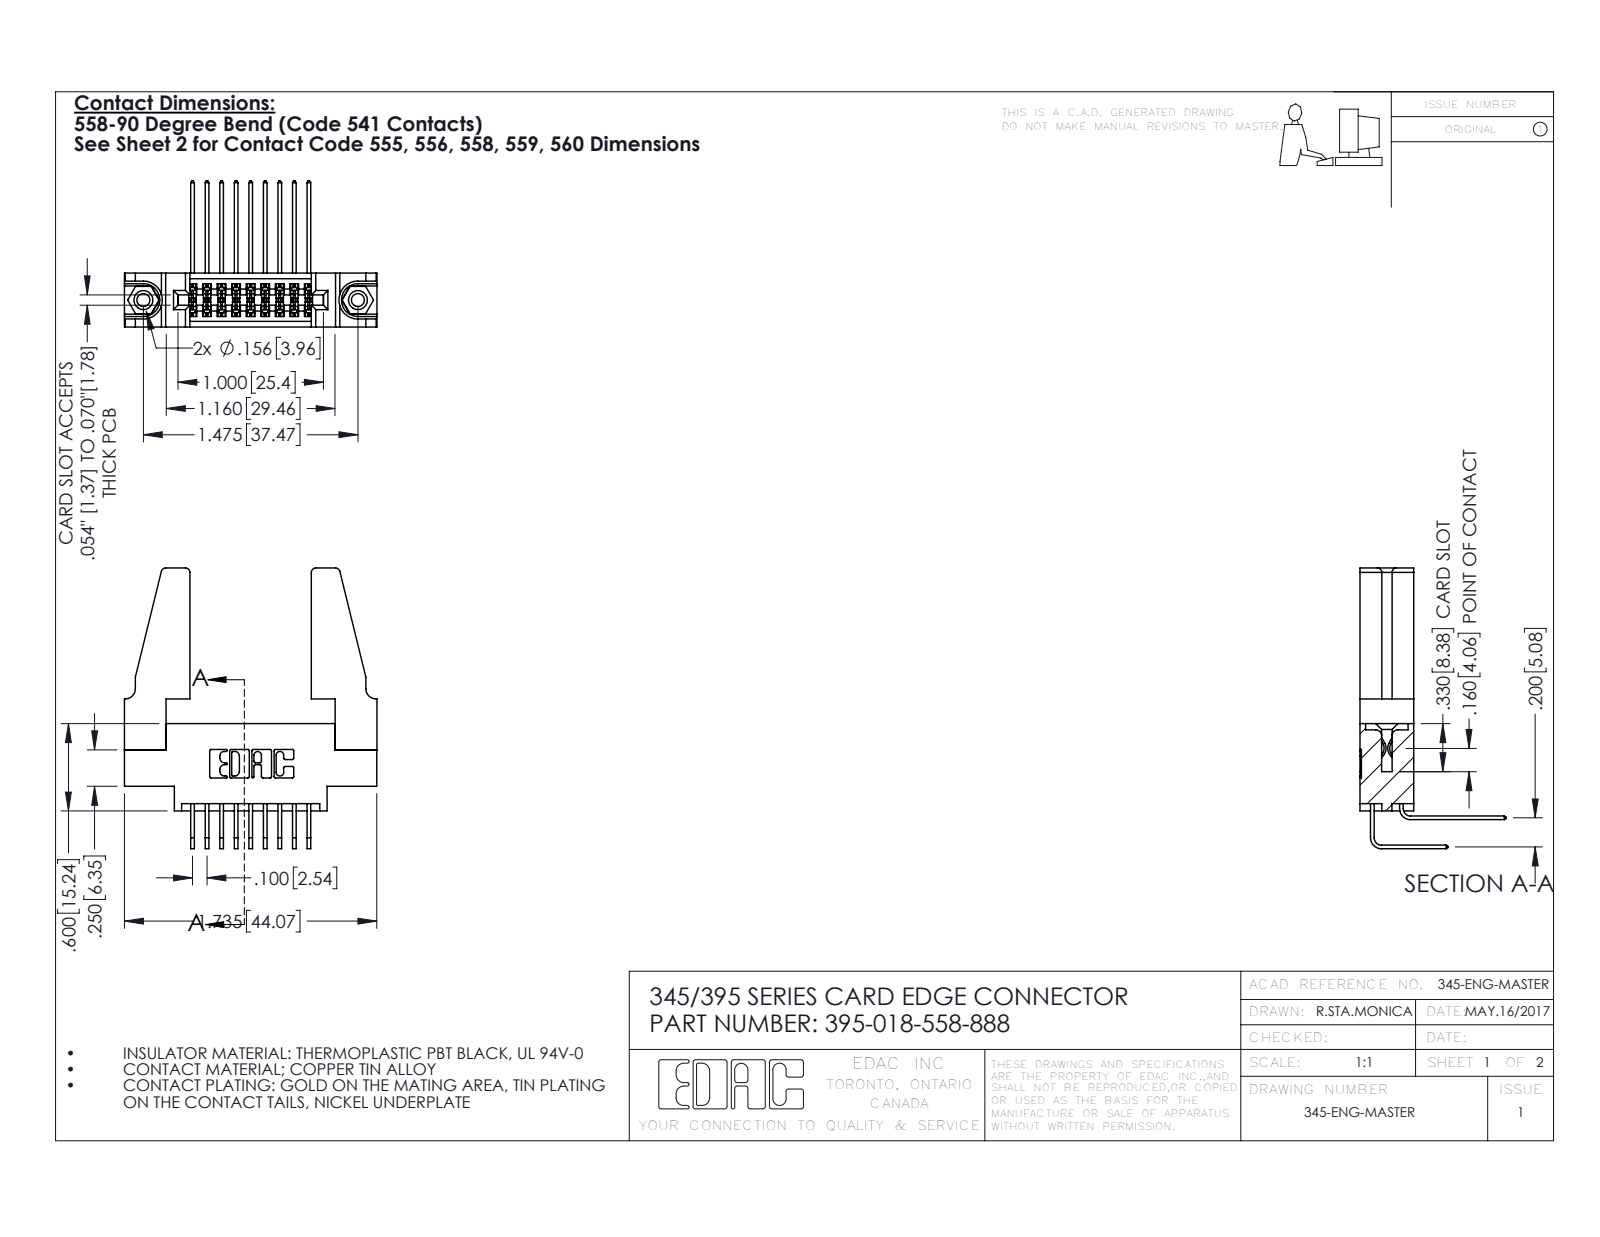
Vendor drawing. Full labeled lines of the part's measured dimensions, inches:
Part name (STEP PRODUCT): 345-292-001_558 Tail - 2; 345-292-001_558 559 Tail - 1; 345 Part_0.170 Offset - 0.156 Dia-TH; 395-018-558-888 (+2 more)
STEP written by: SolidWorks 2016 (CONFIG_CONTROL_DESIGN)
Units: inches
Bodies: 23 solids, 1190 faces (786 planar, 388 cylindrical, 16 other)
Overall size (bounding box): 1.929 × 1.736 × 1.005
Volume: 0.441 in³ · Surface area: 13.92 in²
Round holes (diameter × count): ⌀0.089 ×2, ⌀0.125 ×2, ⌀0.156 ×2, ⌀0.064 ×1
Round bosses / shafts (diameter × count): ⌀0.155 ×2
Partial cylindrical surfaces — rounded edges, fillets, slot ends (radius × count): R0.006 ×28, R0.01 ×22, R0.03 ×8, R0.007 ×6, R0.031 ×6, R0.026 ×3, R0.014 ×2, R0.019 ×2
Main face-to-face distances: 0.37, 0.072, 0.298, 0.2, 0.098, 0.272, 0.025, 0.225, 0.15, 0.148
Hole centre spacings: 0.27, 1.244, 1.475
